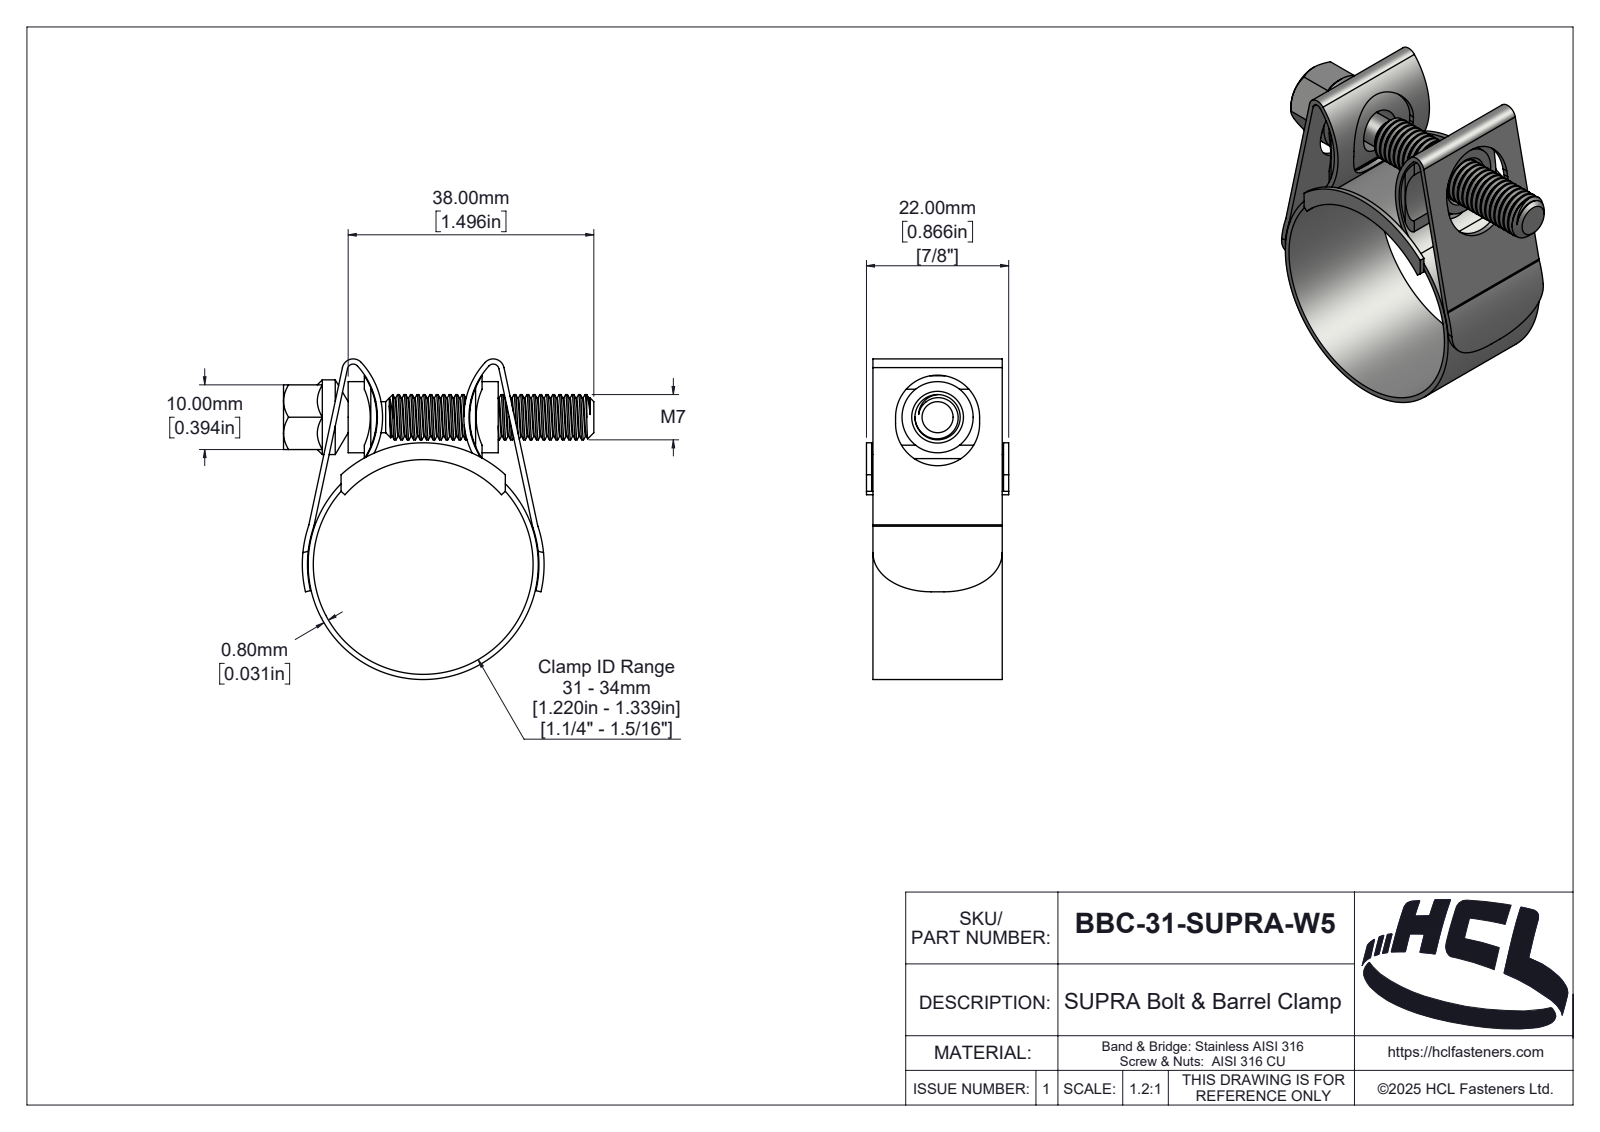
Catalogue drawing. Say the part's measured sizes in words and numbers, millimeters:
The part is named "BBC-31-SUPRA-W5". Its 3-D file was written by "SolidWorks 2025 (AUTOMOTIVE_DESIGN)". It is 5 solids with 300 faces: 46 planar, 174 cylindrical and 80 other. Overall it measures 49.57 by 48 by 22 millimeters. Its volume is 5 962 cubic millimeters and its surface area 11 651 square millimeters. Round holes: 1 of diameter 34. Round bosses or shafts: 1 of diameter 11.55, 1 of diameter 11, 1 of diameter 7, 1 of diameter 4.8. Partial cylindrical surfaces (rounded edges, fillets, slot ends): 4 of radius 1, 2 of radius 0.9, 2 of radius 1.7, 2 of radius 2, 2 of radius 2.8, 2 of radius 6.5, 2 of radius 10.62, 2 of radius 11.62. The main face-to-face distances are 0.81, 20, 1, 21, 10, 0.8, 21.2, 20.2, 2.5, 20.72.
